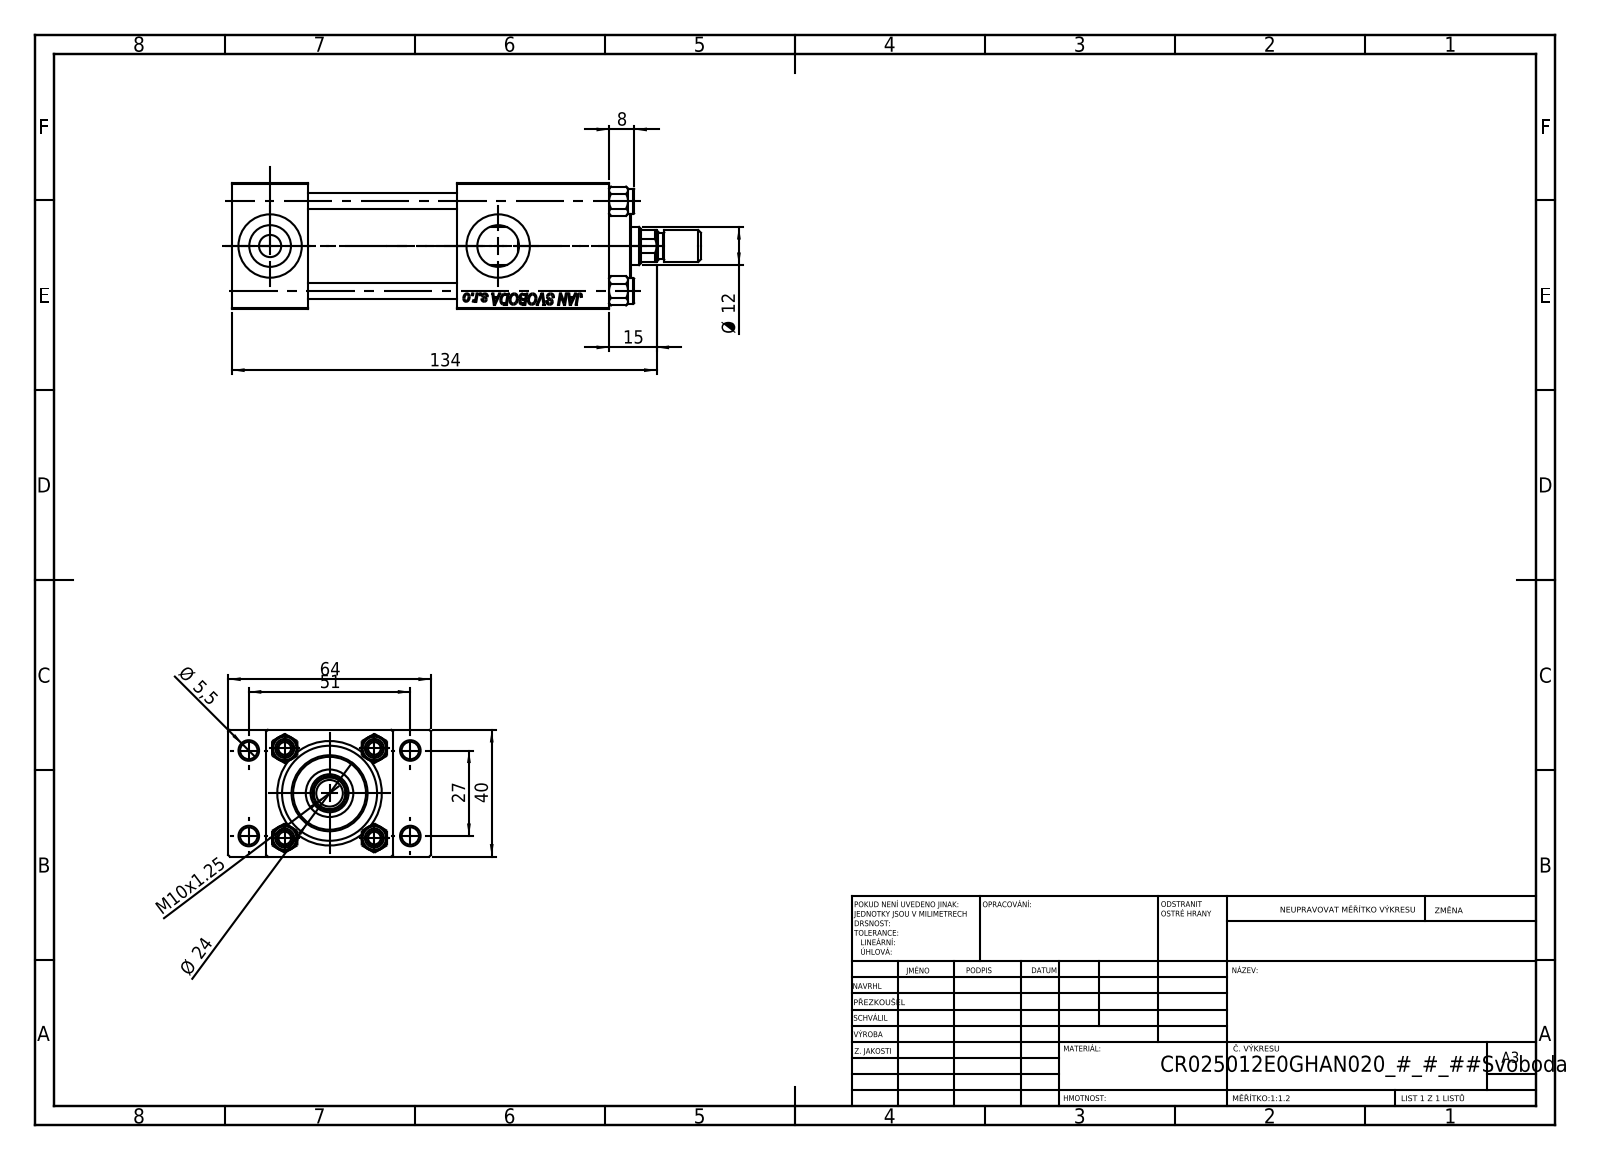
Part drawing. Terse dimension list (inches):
name: NUT_M5_E; V215CR_TYCINKA_E; V215_VC_A; V215CR_VCP_E (+2 more)
written by: SolidWorks 2019 (CONFIG_CONTROL_DESIGN)
unit: in
bodies: 12 solids, 1149 faces (501 planar, 90 cylindrical, 558 other)
size: 5.827 × 2.52 × 1.575
volume: 10.04 in³; area: 97.62 in²
holes: 4× ⌀0.197, 4× ⌀0.217, 3× ⌀0.787, 2× ⌀0.276, 2× ⌀0.518, 1× ⌀0.256, 1× ⌀0.472, 1× ⌀0.591, 1× ⌀0.984, 1× ⌀1.181
bosses: 5× ⌀0.315, 1× ⌀1.22, 1× ⌀0.945, 1× ⌀0.394
rounds: 1× R0.217
face distances: 1.575, 0.945, 0.472, 2.047, 4.685, 3.74, 3.555, 2.61, 1.13, 1.85
hole spacings: 0.448, 0.788, 1.114, 1.136, 1.177, 1.561, 1.903, 1.063
